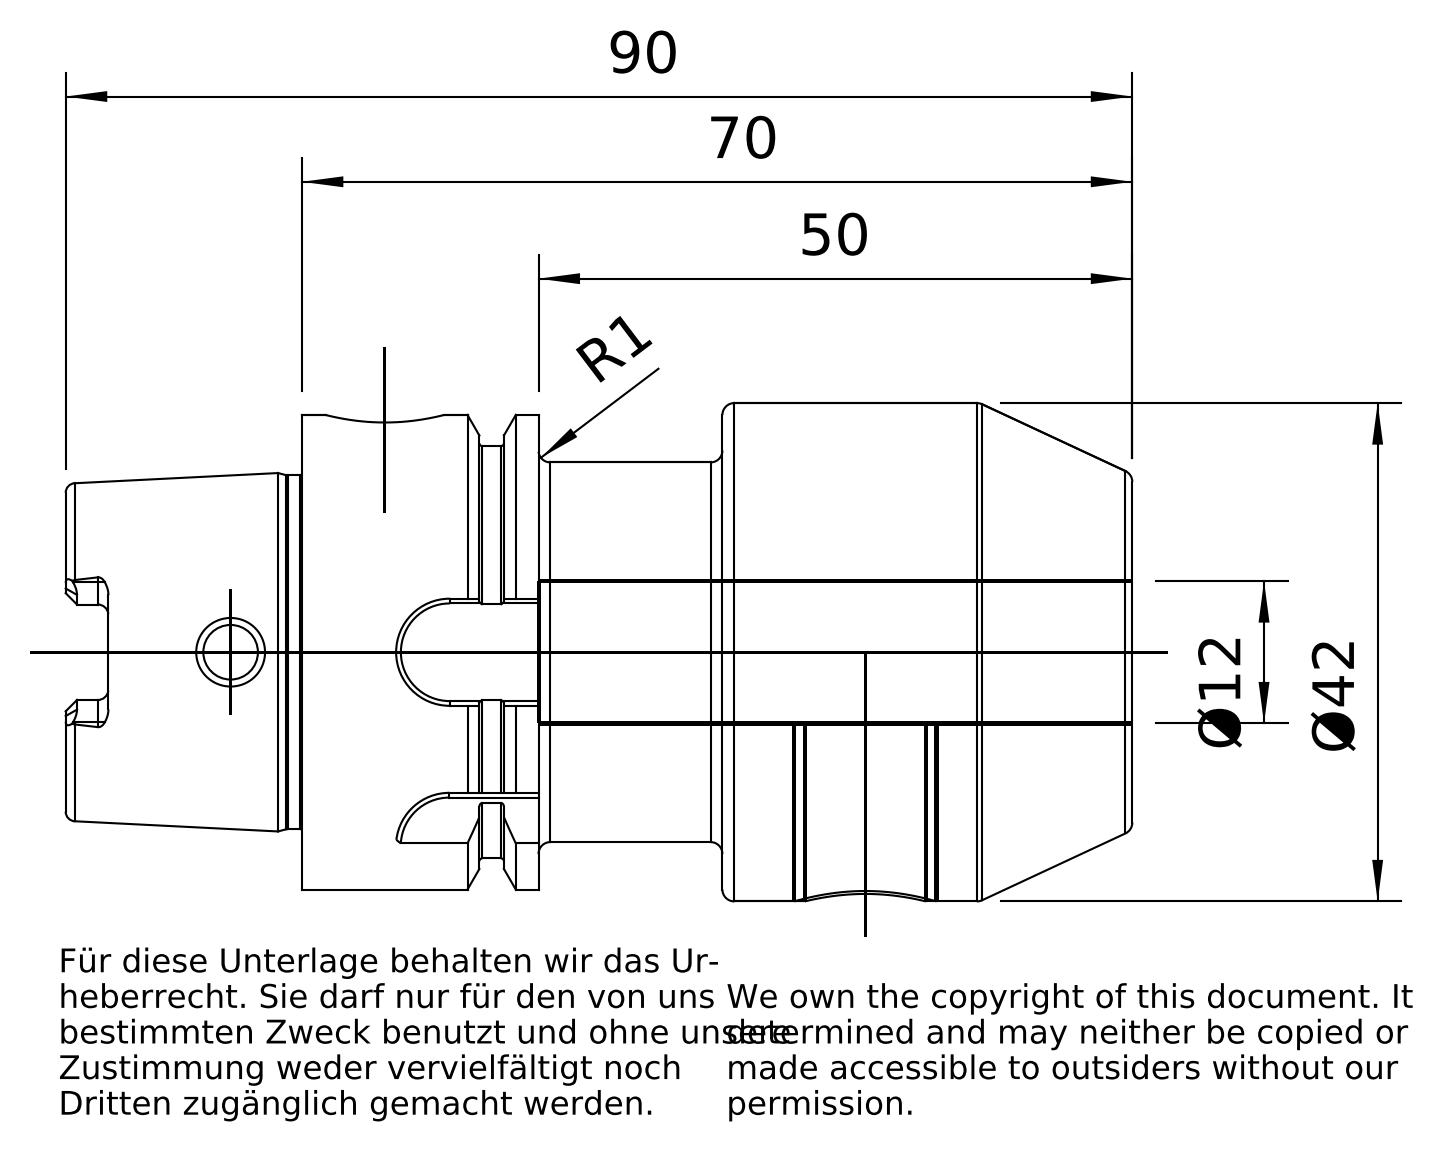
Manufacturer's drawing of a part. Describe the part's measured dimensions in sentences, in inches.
The part is named "A40-000-12". Its 3-D file was written by "PRO/ENGINEER BY PARAMETRIC TECHNOLOGY CORPORATION, 2010430 (CONFIG_CONTROL_DESIGN)". It is 1 solid with 198 faces: 62 planar, 56 cylindrical and 80 other. Overall it measures 3.539 by 1.654 by 1.654 inches. Its volume is 4.449 cubic inches and its surface area 29.36 square inches. Round holes: 2 of diameter 0.402, 2 of diameter 0.472, 1 of diameter 0.181, 1 of diameter 0.394, 1 of diameter 0.481, 1 of diameter 0.492, 1 of diameter 0.828, 1 of diameter 1.007. Round bosses or shafts: 1 of diameter 1.654, 1 of diameter 1.575, 1 of diameter 1.368, 1 of diameter 1.26, 1 of diameter 1.174. Partial cylindrical surfaces (rounded edges, fillets, slot ends): 6 of radius 0.035, 4 of radius 0.074, 3 of radius 0.177, 1 of radius 0.178. The main face-to-face distances are 2.756, 1.396, 1.36, 0.785, 0.61, 1.97, 0.313, 0.472, 1.083, 2.443. The hole center spacings are 1.594.
